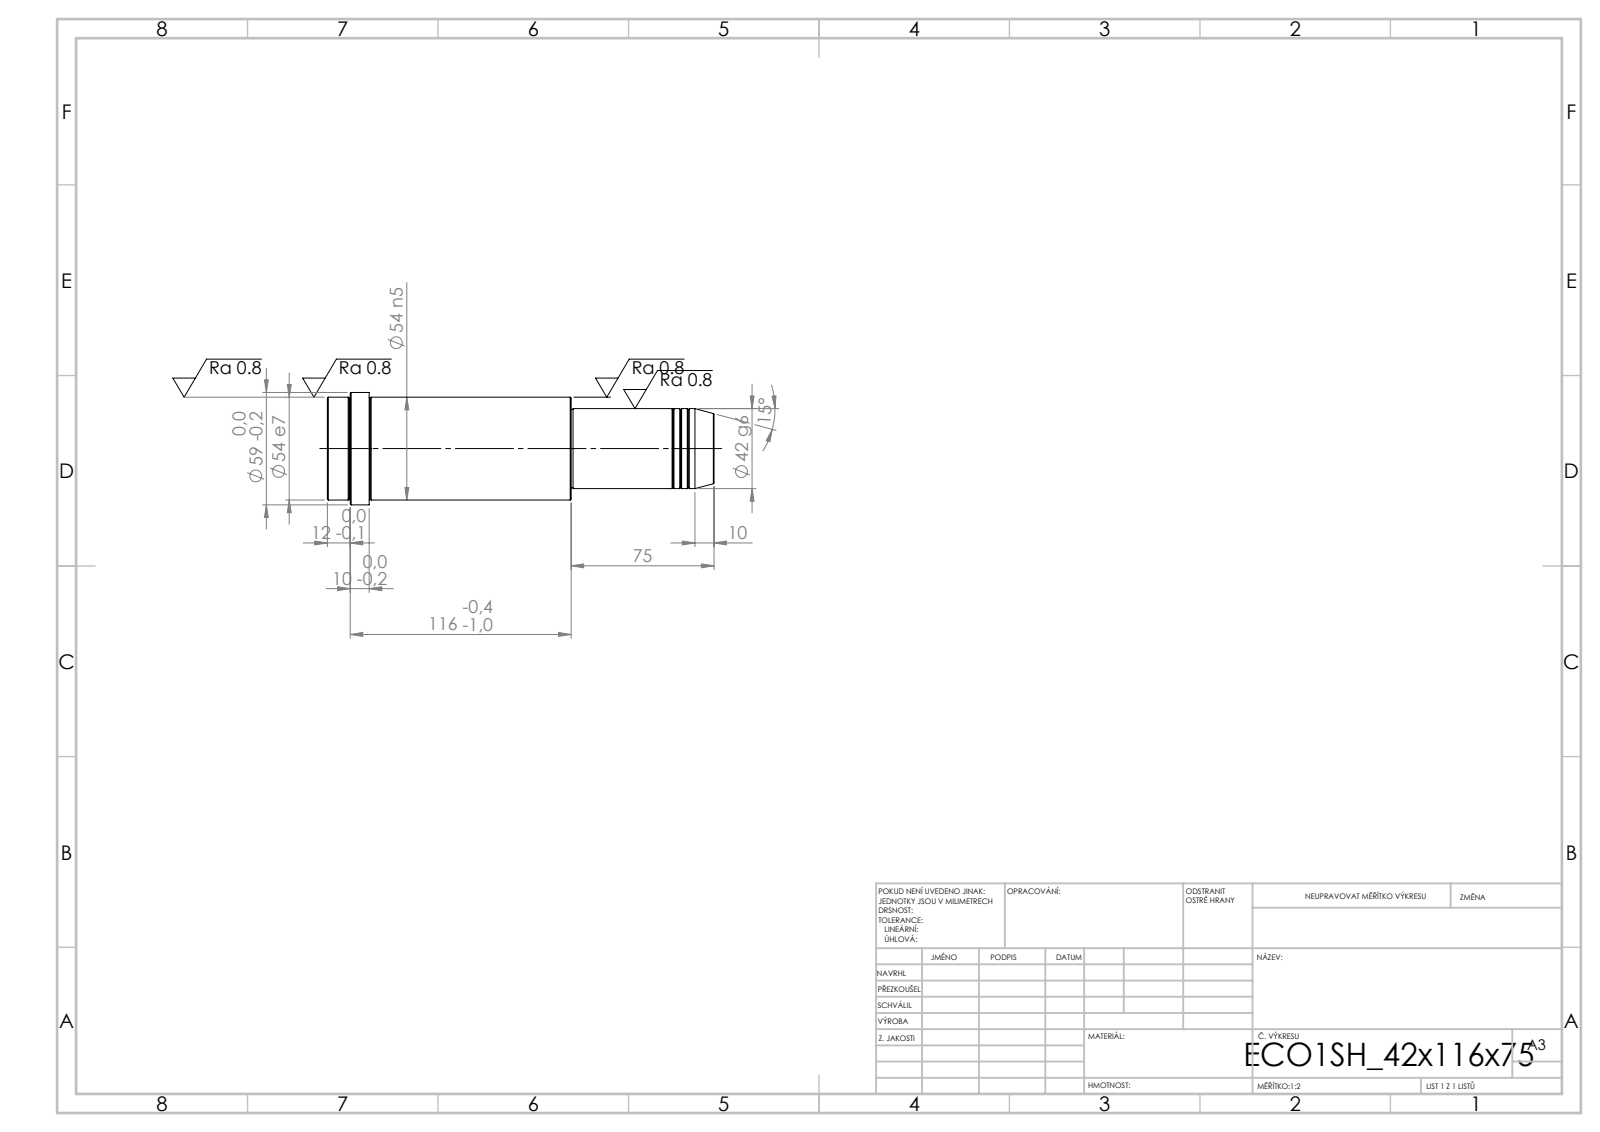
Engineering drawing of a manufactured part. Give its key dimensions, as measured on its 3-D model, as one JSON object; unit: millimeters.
{"step_written_by": "SolidWorks 2019 (CONFIG_CONTROL_DESIGN)", "units": "millimeters", "bodies": {"solids": 1, "faces": 52, "planar": 6, "cylindrical": 16, "other": 30}, "overall_size": [203, 59, 59], "volume_mm3": 399382, "surface_area_mm2": 37228, "round_bosses_or_shafts": [[59, 1], [54, 1], [42, 1], [41, 1]], "face_to_face_distances": [203, 75, 128, 181, 106, 22, 191, 116, 10, 12]}
